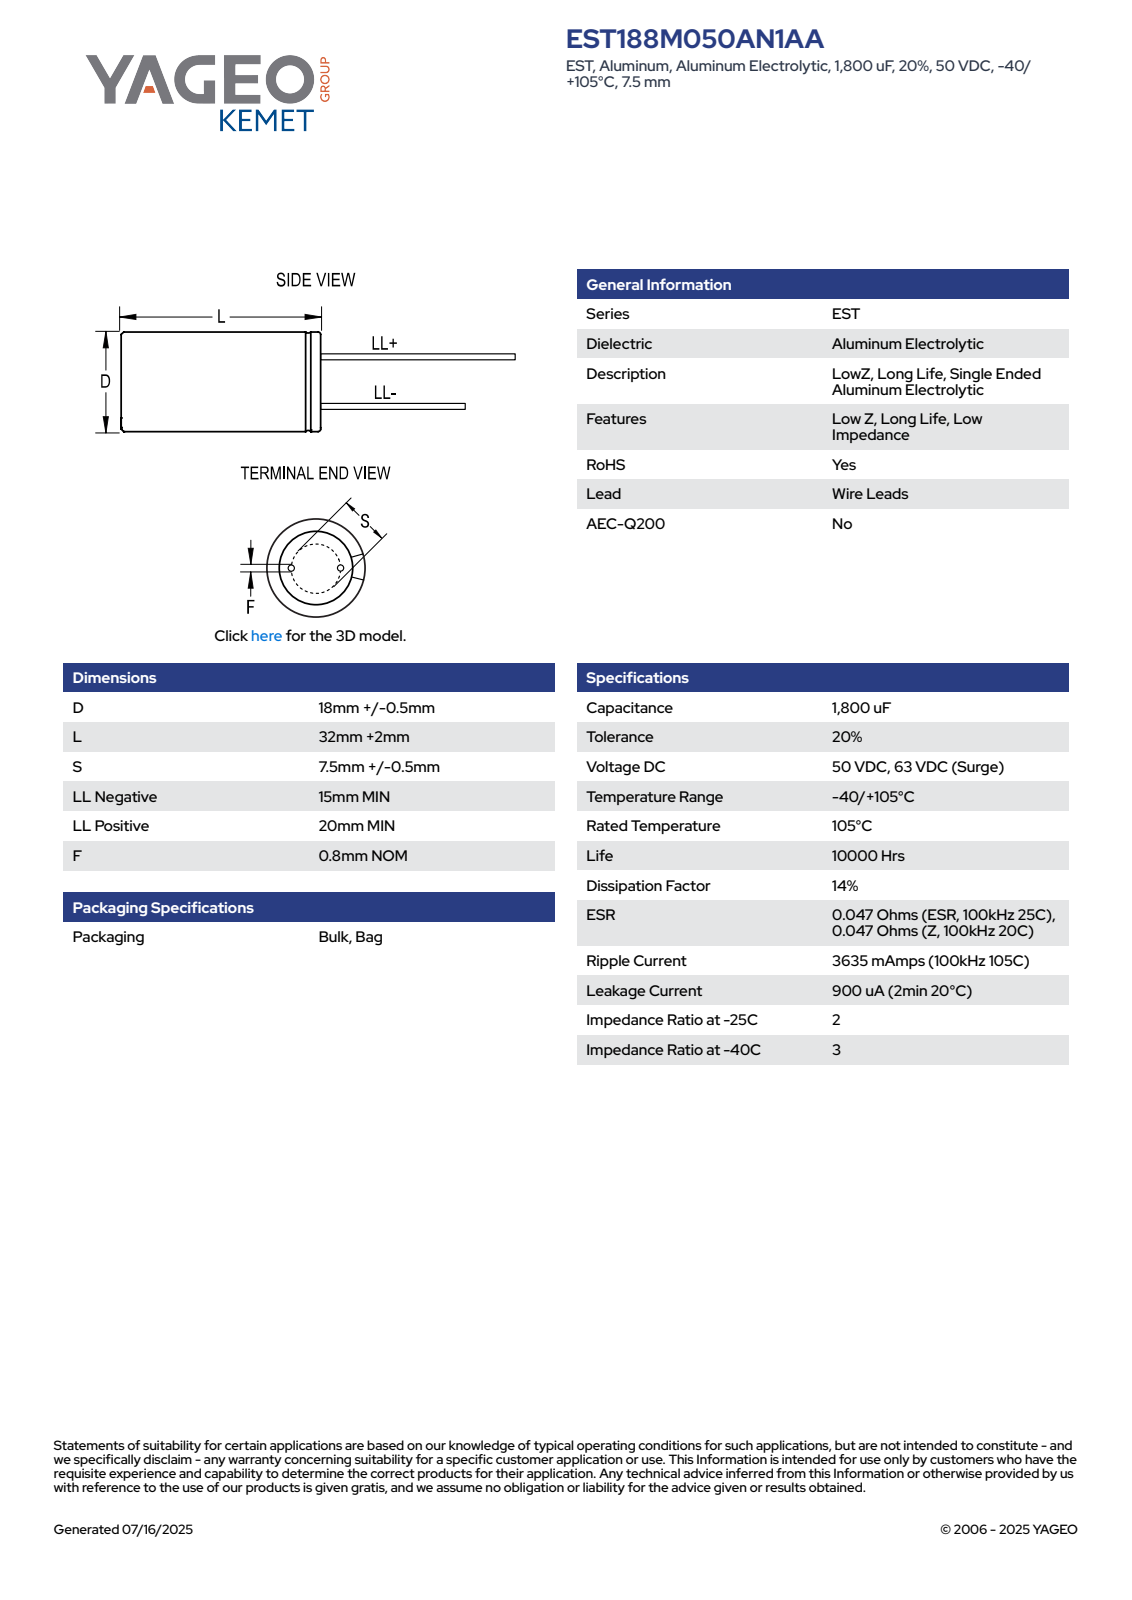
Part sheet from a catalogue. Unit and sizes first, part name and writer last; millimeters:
Units: millimetres
Overall size (bounding box): 54.01 × 18.5 × 18.5
Round bosses / shafts (diameter × count): ⌀0.8 ×2, ⌀18.5 ×1
Main face-to-face distances: 34, 34.01, 49.01, 54.01, 49, 54, 15, 20, 5, 2.48
Volume: 9 091 mm³ · Surface area: 2 682 mm²
Bodies: 4 solids, 75 faces (61 planar, 8 cylindrical, 6 other)
Part name (STEP PRODUCT): CAR_KLP_18X32_D18.5L34S7.5F0.8
STEP written by: SolidWorks 2014 (AUTOMOTIVE_DESIGN)
